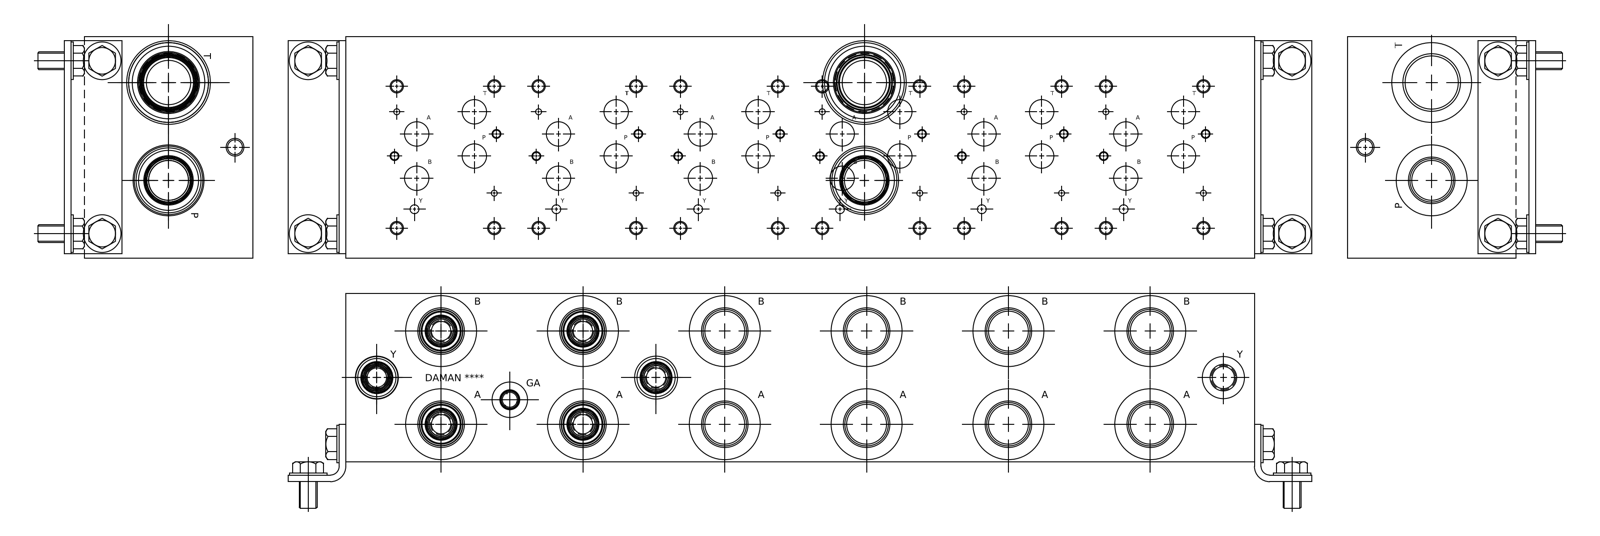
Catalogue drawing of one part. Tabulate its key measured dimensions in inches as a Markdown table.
| quantity | value |
| --- | --- |
| part name | Part_AD07HP064S_3D |
| STEP written by | Autodesk Inventor 2020 (CONFIG_CONTROL_DESIGN) |
| units | inches |
| bodies | 1 solid, 1157 faces (543 planar, 233 cylindrical, 381 other) |
| overall size | 25.624 × 6.25 × 4.75 |
| volume | 720.7 in³ |
| surface area | 789.3 in² |
| round holes (diameter × count) | 0.75 × 26, 0.312 × 24, 0.375 × 24, 1.063 × 13, 1.231 × 13, 1.329 × 13, 1.934 × 13, 0.171 × 12, 0.201 × 12, 0.25 × 12, 1.313 × 12, 1.398 × 12 |
| main face-to-face distances | 4.75, 6.25, 0.031, 25.624, 6.219, 25.593, 25.562, 0.75, 0.781, 5.469 |
| hole center spacings | 4, 8, 12, 4.785, 4.854, 16, 4.064, 4.119 |
